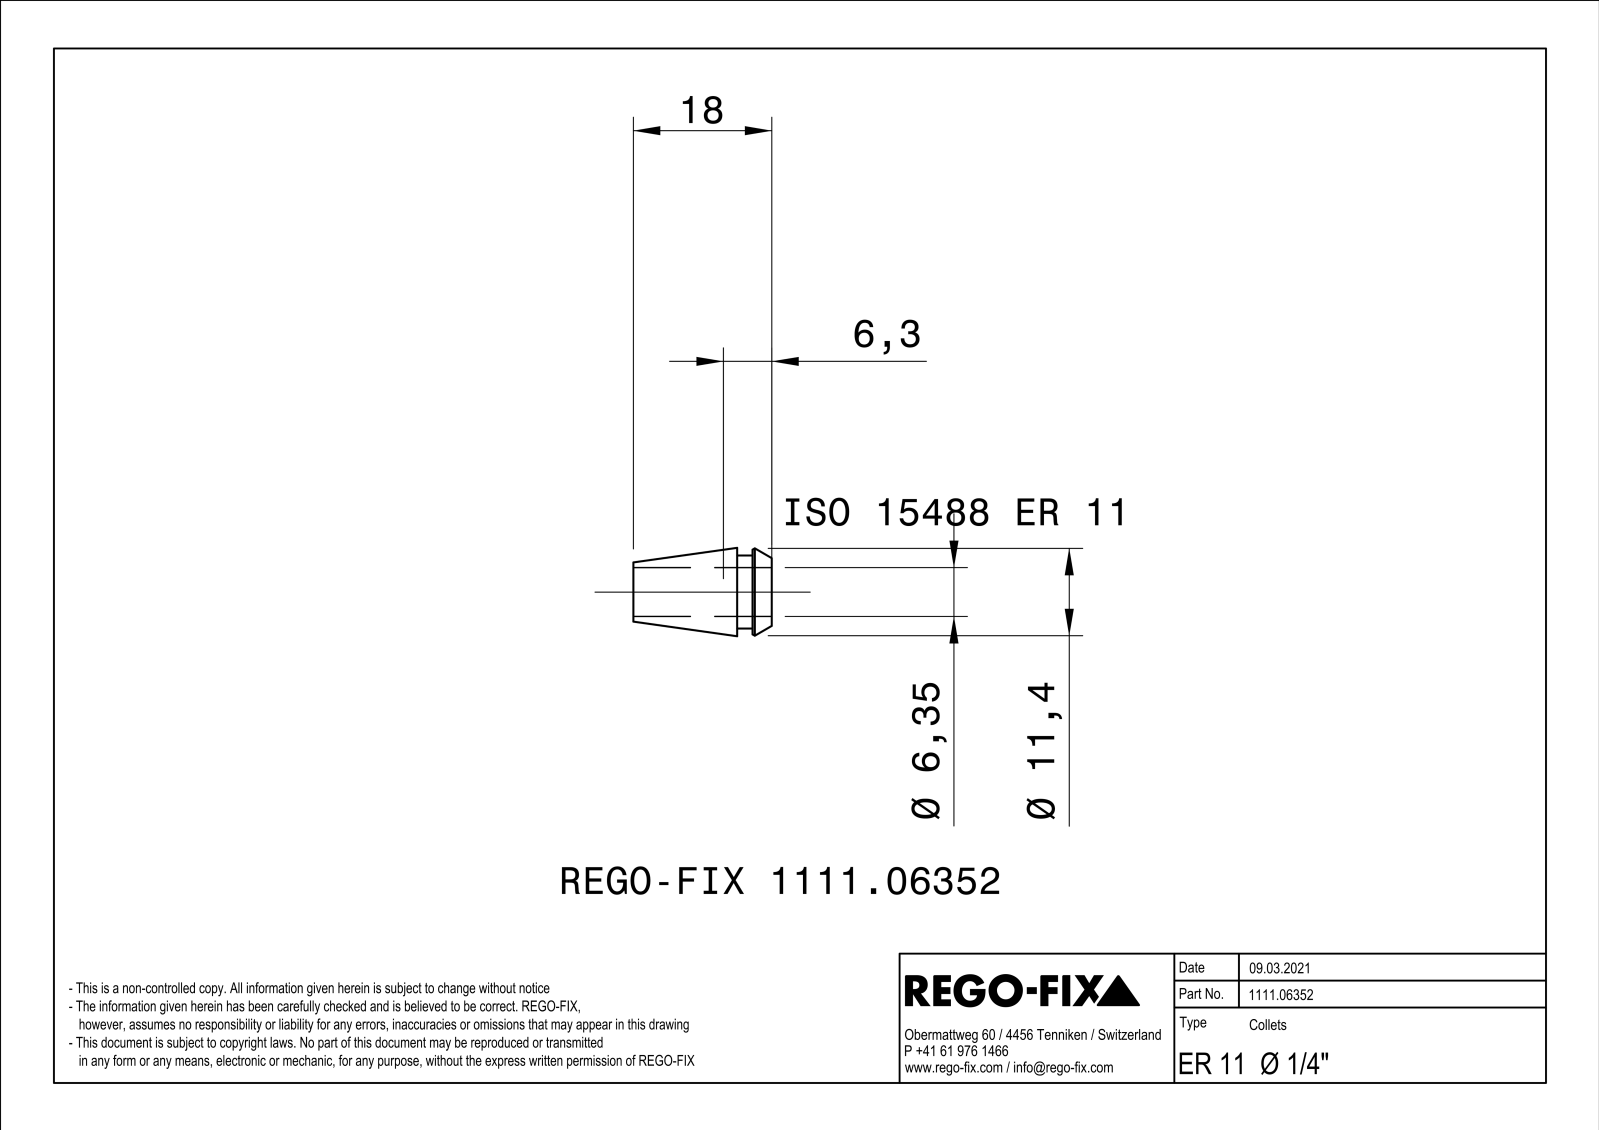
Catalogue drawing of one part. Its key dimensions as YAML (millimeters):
part_name: "NOCUT"
step_written_by: "SIEMENS PLM Software Solid Edge ST10 (AUTOMOTIVE_DESIGN)"
units: millimeters
bodies: {solids: 1, faces: 157, planar: 66, cylindrical: 37, other: 54}
overall_size: [18, 11.5, 11.49]
volume: 637
surface_area: 1454
round_holes:
  - {diameter: 6.35, count: 1}
round_bosses_or_shafts:
  - {diameter: 11.5, count: 1}
  - {diameter: 9.5, count: 1}
partial_cylinders:
  - {radius: 25, count: 12}
face_to_face_distances: [0.45, 0.46, 0.44, 2, 2.5, 4.5, 4, 14, 18, 15.5]
